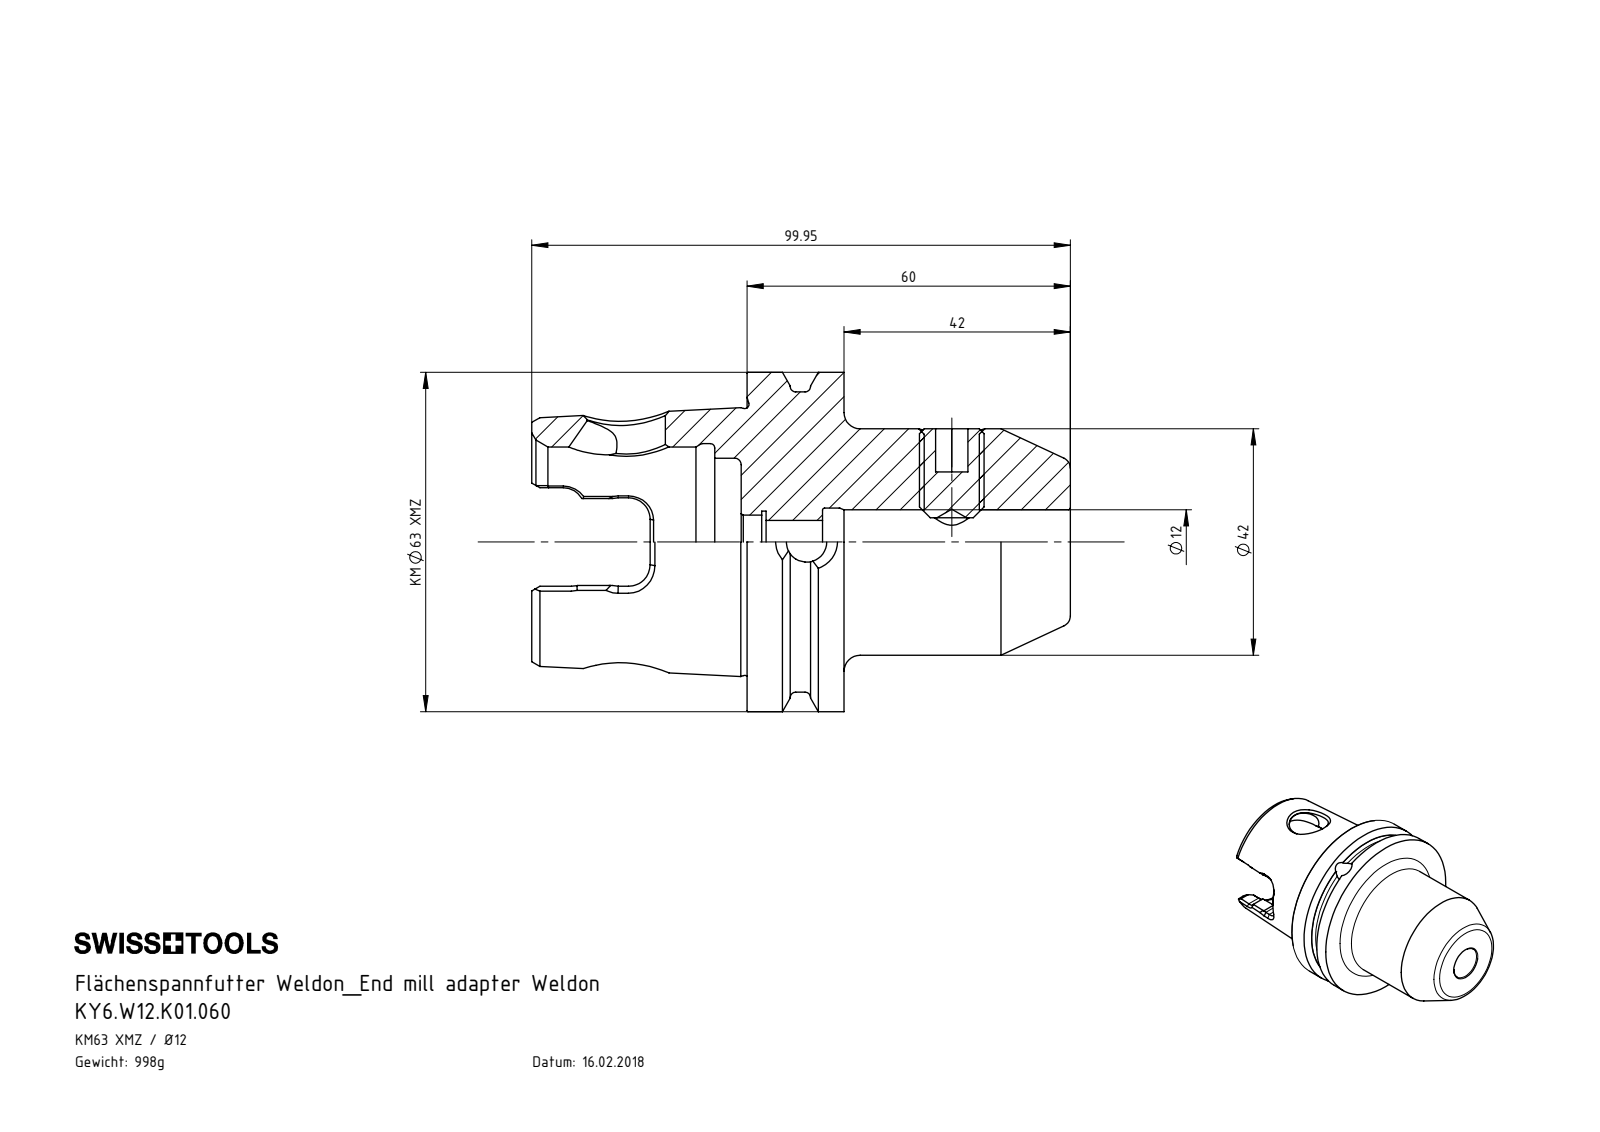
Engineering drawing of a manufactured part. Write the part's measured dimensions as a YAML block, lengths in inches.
part_name: "KY6.W12.K01.060; W12-ER1.001.016; KY6-W12.K01.060_A"
step_written_by: "SolidWorks 2017 (CONFIG_CONTROL_DESIGN)"
units: inches
bodies: {solids: 2, faces: 242, planar: 55, cylindrical: 56, other: 131}
overall_size: [3.935, 2.478, 2.478]
volume: 7.762
surface_area: 42.84
round_holes:
  - {diameter: 0.294, count: 2}
  - {diameter: 0.315, count: 1}
  - {diameter: 0.334, count: 1}
  - {diameter: 0.394, count: 1}
  - {diameter: 0.404, count: 1}
  - {diameter: 0.453, count: 1}
  - {diameter: 0.472, count: 1}
  - {diameter: 0.496, count: 1}
  - {diameter: 0.571, count: 1}
  - {diameter: 1.224, count: 1}
  - {diameter: 1.389, count: 1}
  - {diameter: 1.437, count: 1}
round_bosses_or_shafts:
  - {diameter: 2.478, count: 1}
  - {diameter: 2.193, count: 1}
  - {diameter: 1.654, count: 1}
  - {diameter: 0.472, count: 1}
partial_cylinders:
  - {radius: 0.157, count: 6}
  - {radius: 0.277, count: 2}
face_to_face_distances: [0.709, 0.043, 0.752, 2.406, 2.362, 1.654, 0.236, 0.193, 0.945, 2.598]
hole_center_spacings: [2.378]
